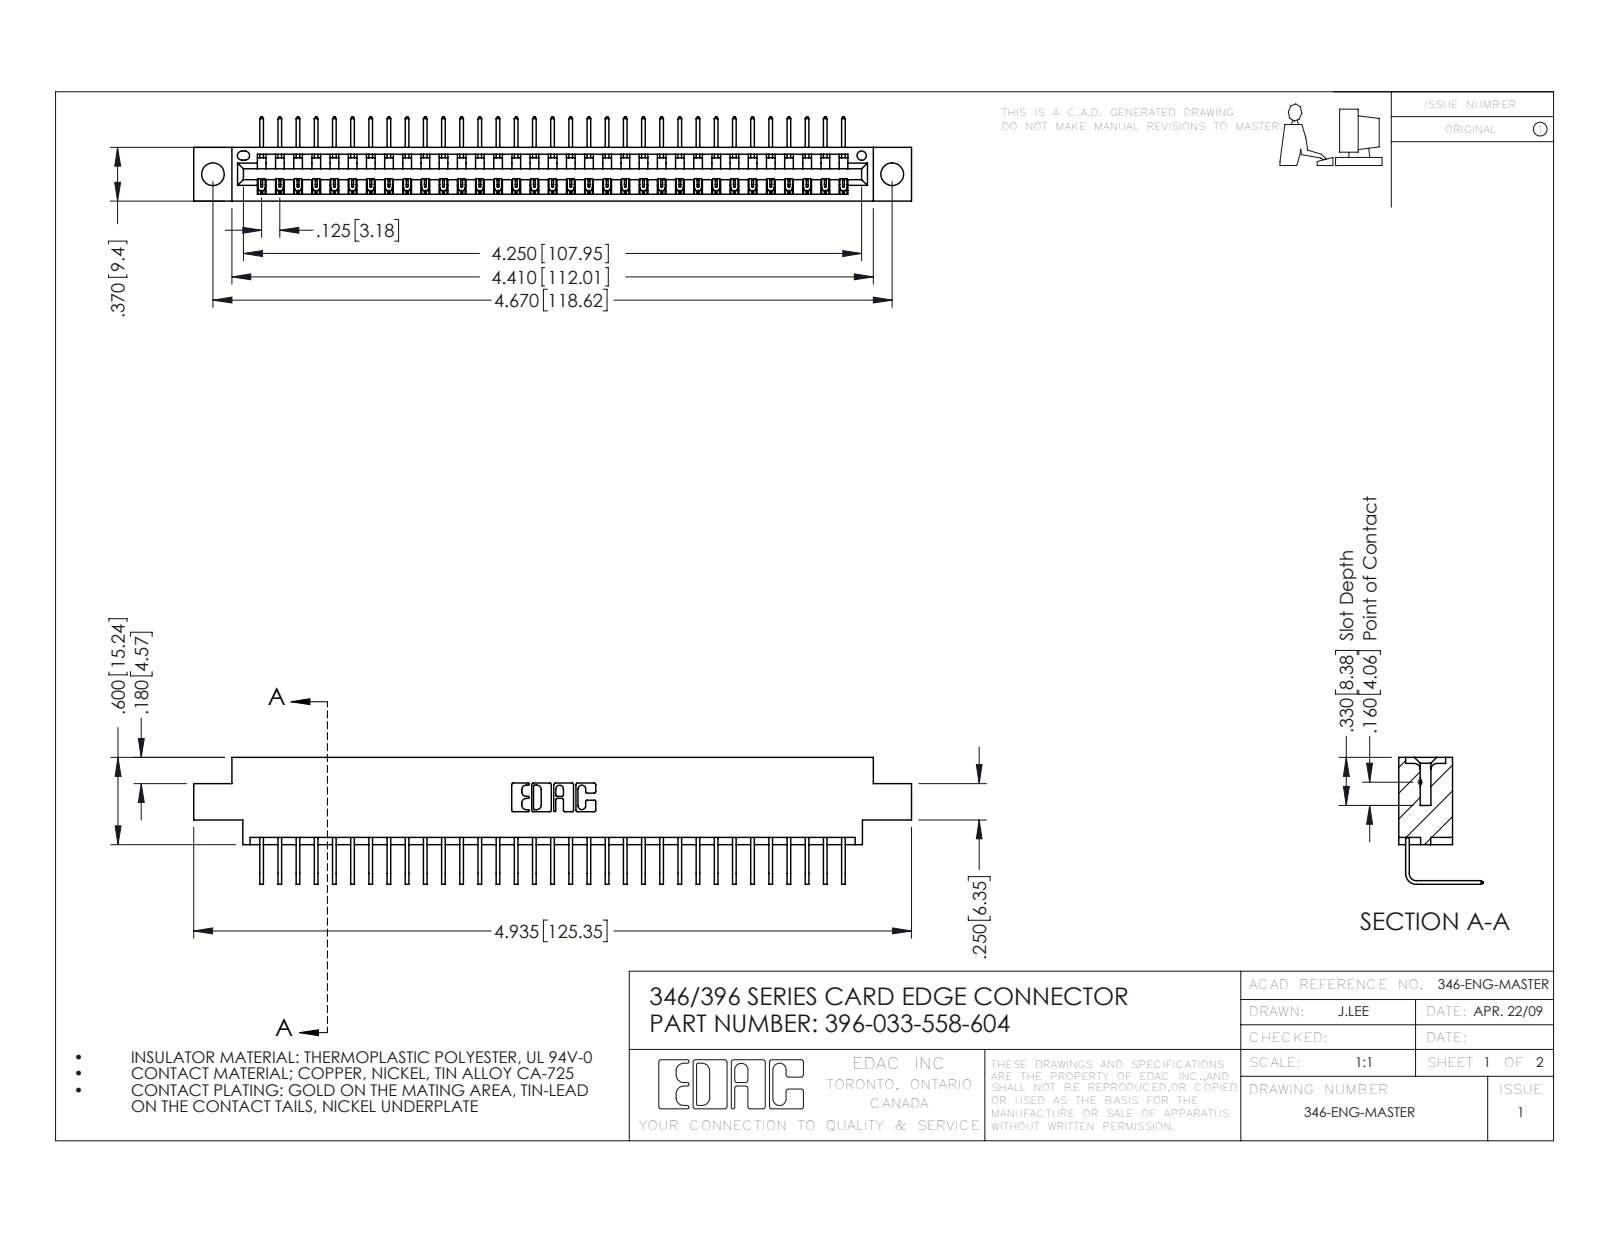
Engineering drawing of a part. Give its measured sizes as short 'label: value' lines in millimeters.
name: 345-292-001_558 Tail - 2; 396-033-558-604; 346 Part_0.170 Offset - 0.156 Dia-TH
written by: SolidWorks 2016 (CONFIG_CONTROL_DESIGN)
unit: mm
bodies: 34 solids, 2106 faces (1466 planar, 640 cylindrical, 0 other)
size: 125.3 × 22.2 × 14.7
volume: 11 800 mm³; area: 15 280 mm²
holes: 2× ⌀4, 1× ⌀1.6
rounds: 66× R0.2, 22× R0.3, 6× R0.2, 6× R0.8, 3× R0.7, 2× R0.8, 2× R1, 1× R0.4
face distances: 8.2, 1.2, 9.4, 6.4, 7.6, 0.6, 1.8, 3.8, 5.6, 2.5
hole spacings: 6.2, 113.3, 118.6
